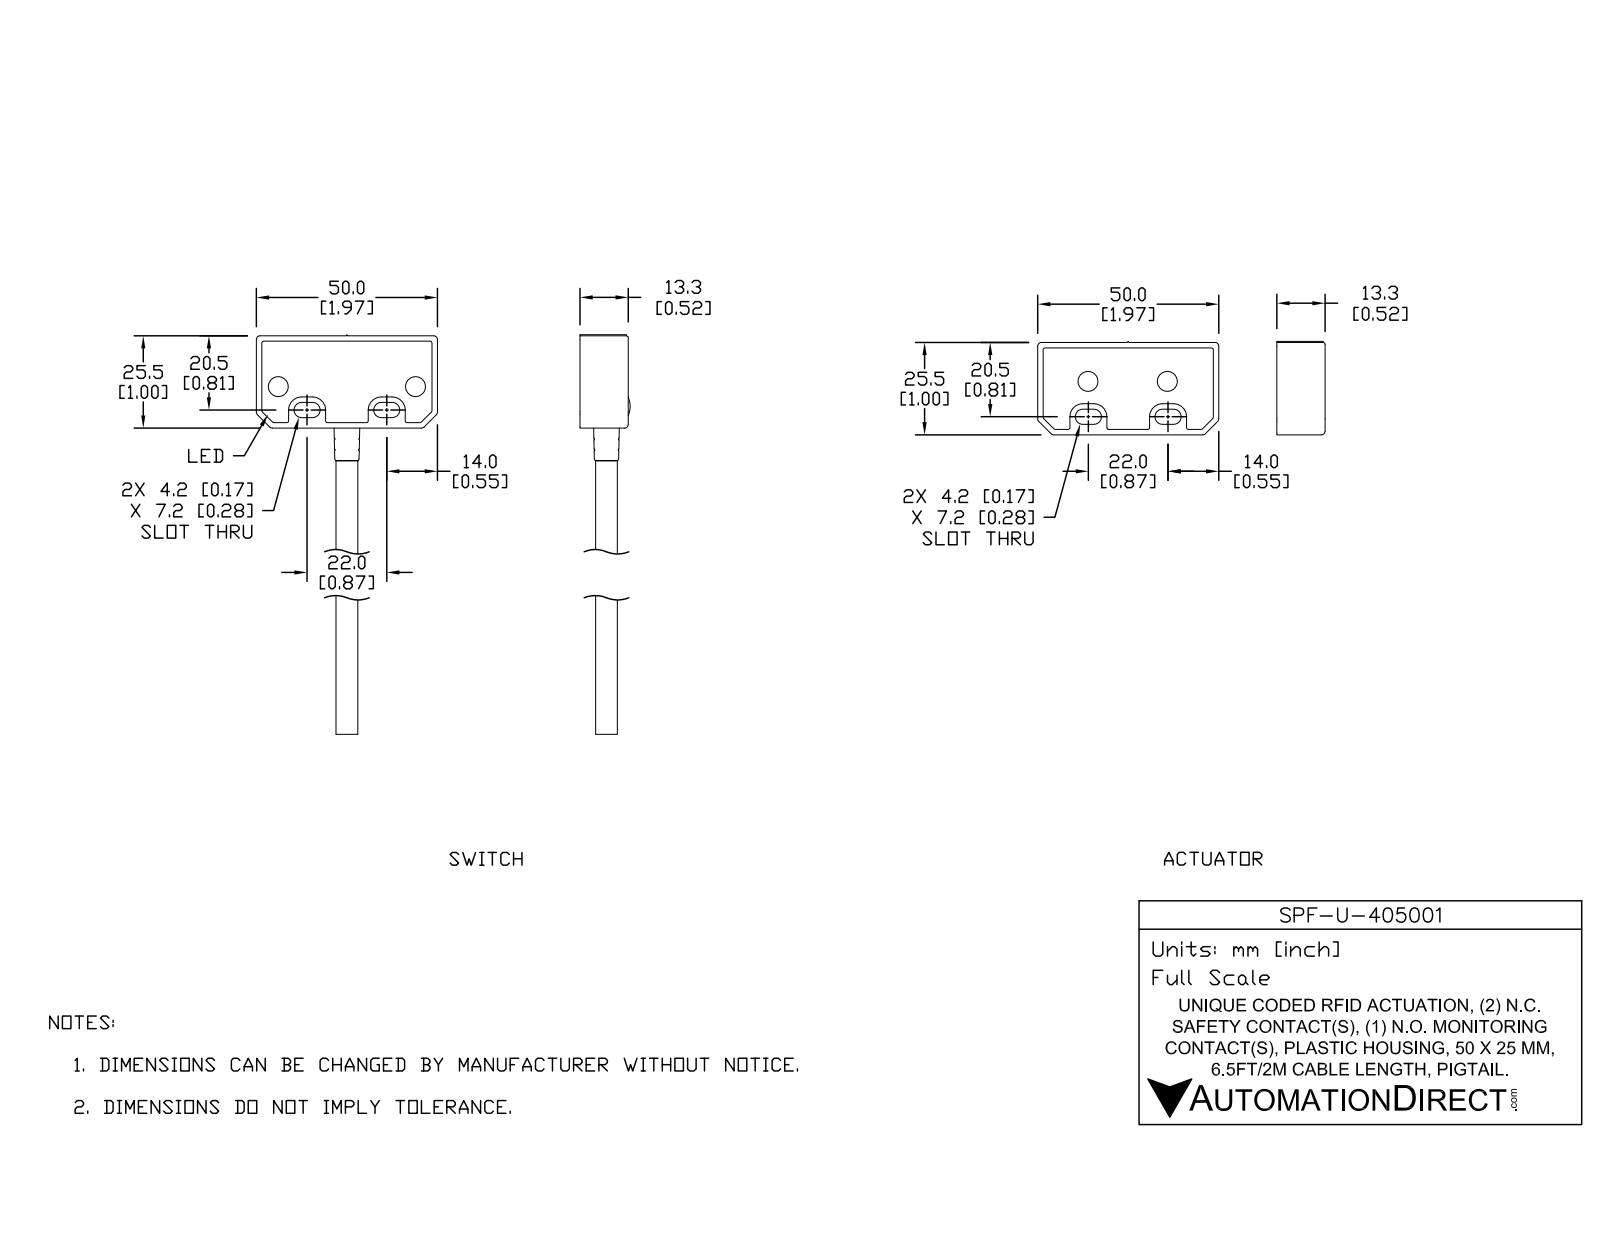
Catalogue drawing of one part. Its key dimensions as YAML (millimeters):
part_name: "SPF-U-405001; SPF-U-405001_2; SPF-U-405001_1"
step_written_by: "SolidWorks 2017 (AUTOMOTIVE_DESIGN)"
units: millimeters
bodies: {solids: 12, faces: 1147, planar: 475, cylindrical: 358, other: 314}
overall_size: [205.5, 50, 13.8]
volume: 18110
surface_area: 23430
round_holes:
  - {diameter: 5, count: 4}
  - {diameter: 3, count: 1}
  - {diameter: 4.4, count: 1}
  - {diameter: 5.4, count: 1}
  - {diameter: 5.9, count: 1}
  - {diameter: 7, count: 1}
round_bosses_or_shafts:
  - {diameter: 2, count: 4}
  - {diameter: 4.9, count: 2}
  - {diameter: 0.8, count: 2}
  - {diameter: 8.6, count: 1}
  - {diameter: 7.6, count: 1}
  - {diameter: 7.1, count: 1}
  - {diameter: 6, count: 1}
  - {diameter: 5.3, count: 1}
partial_cylinders:
  - {radius: 0.5, count: 132}
  - {radius: 1, count: 36}
  - {radius: 2, count: 8}
  - {radius: 2.1, count: 8}
  - {radius: 3.6, count: 8}
  - {radius: 4.6, count: 8}
  - {radius: 0.3, count: 6}
  - {radius: 3.6, count: 4}
face_to_face_distances: [1.5, 11.6, 10.1, 1.2, 11.3, 12.8, 26.5, 2.5, 24, 48.5]
hole_center_spacings: [5.6, 21.9, 27, 27.1, 32.6, 37.9, 39.4, 39.6]
